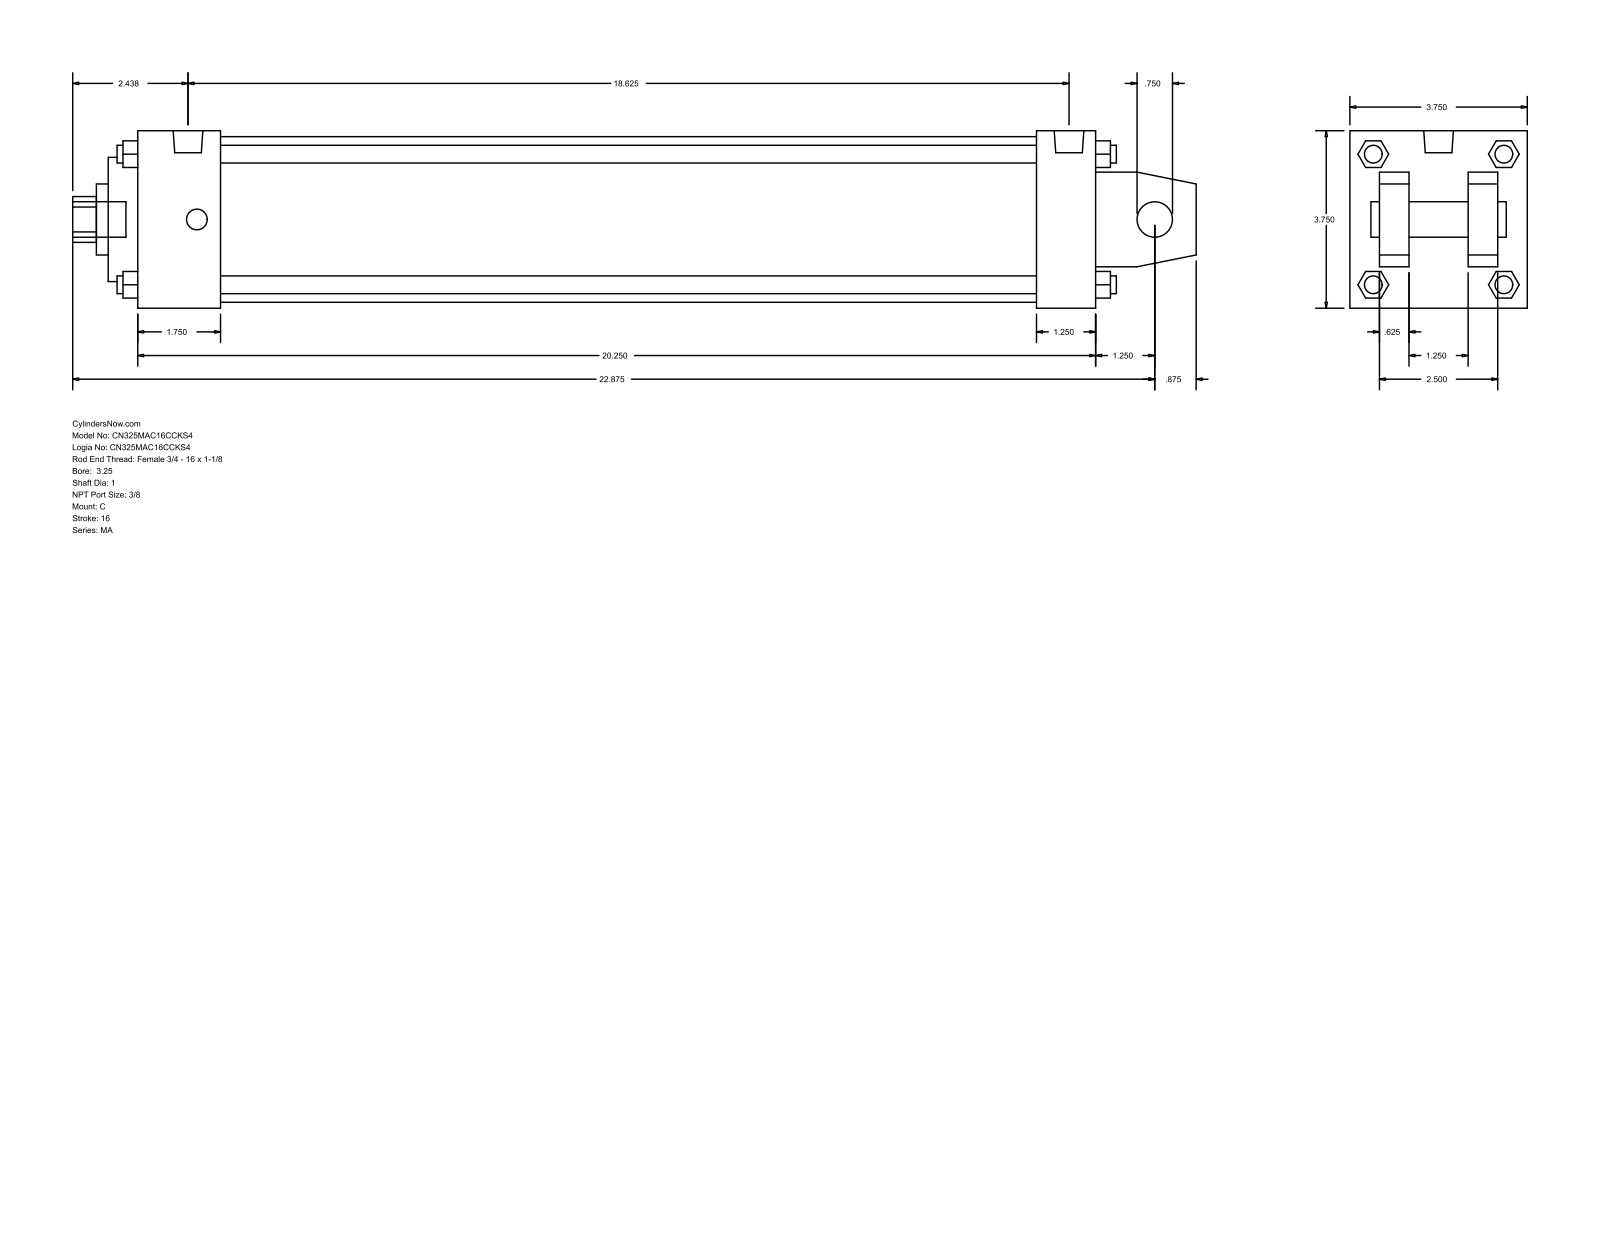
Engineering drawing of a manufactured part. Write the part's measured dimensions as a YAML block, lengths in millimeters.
part_name: "MA_C__0325_1"
step_written_by: "GSSL Pune (CONFIG_CONTROL_DESIGN)"
units: millimeters
bodies: {solids: 0, faces: 141, planar: 109, cylindrical: 32, other: 0}
overall_size: [603.25, 95.25, 95.25]
round_holes:
  - {diameter: 19.05, count: 1}
  - {diameter: 25.4, count: 1}
  - {diameter: 38.1, count: 1}
  - {diameter: 66.67, count: 1}
  - {diameter: 88.9, count: 1}
round_bosses_or_shafts:
  - {diameter: 11.11, count: 4}
  - {diameter: 9.53, count: 4}
  - {diameter: 15.93, count: 2}
  - {diameter: 19.05, count: 1}
partial_cylinders:
  - {radius: 12.29, count: 1}
face_to_face_distances: [95.24, 15.87, 63.5, 514.35, 31.74, 79.37, 47.63, 530.22, 482.6, 31.75]
